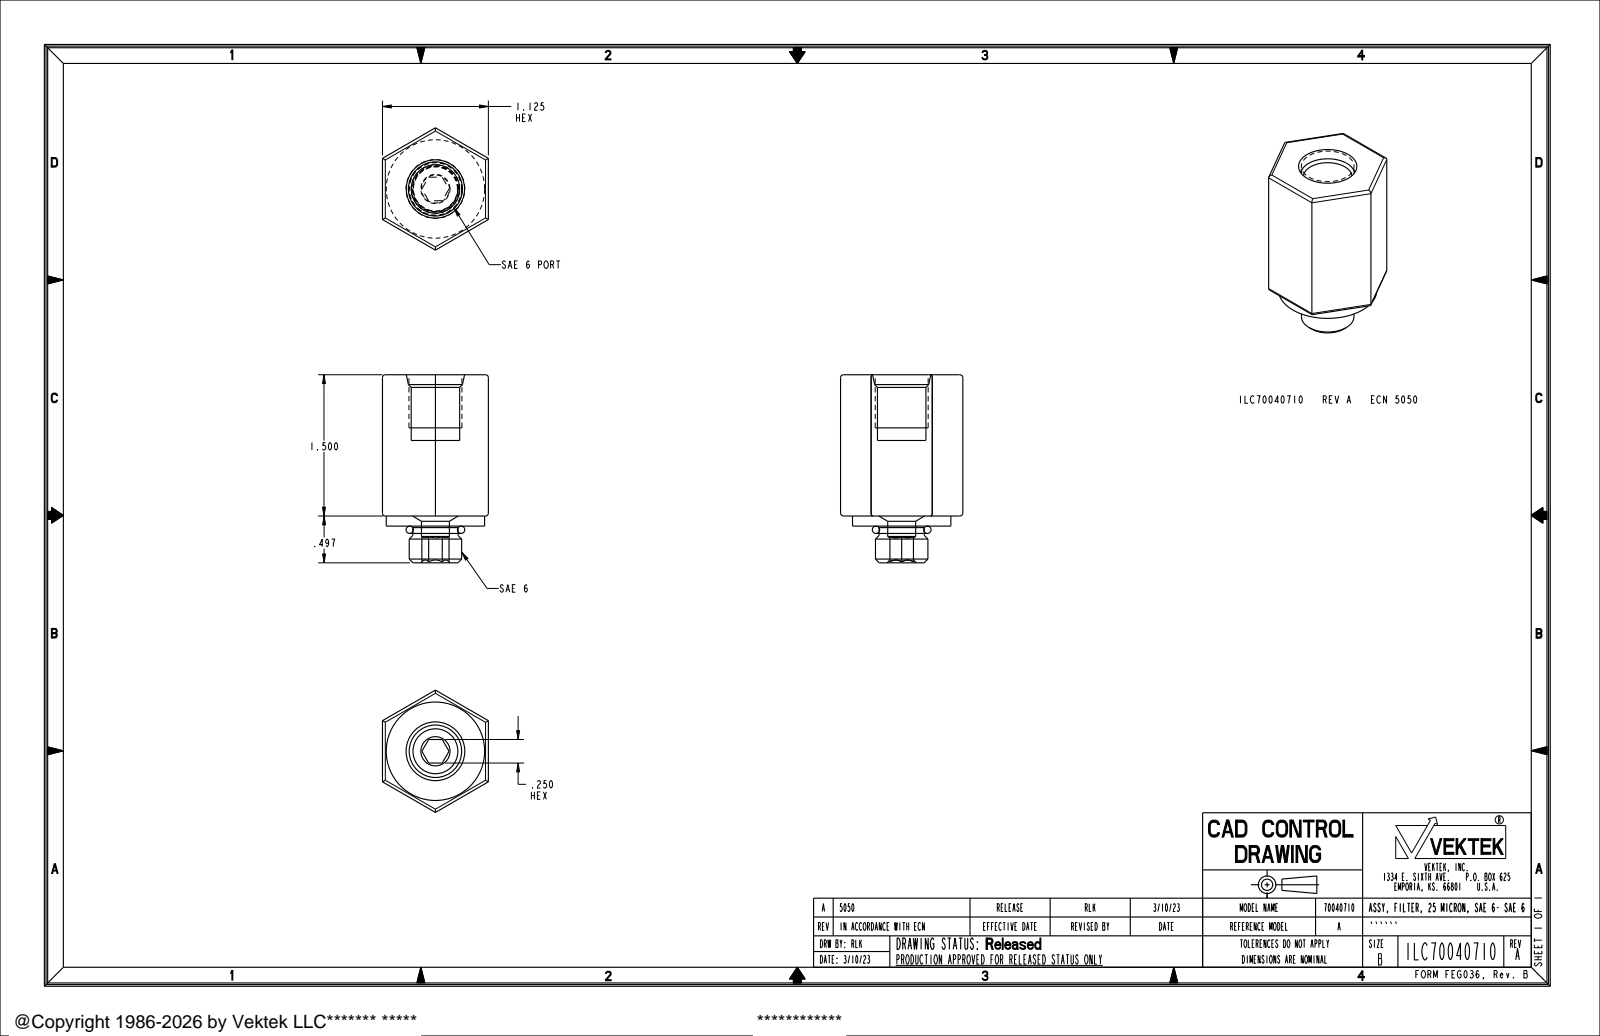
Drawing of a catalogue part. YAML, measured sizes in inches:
part_name: "ILC70040710"
step_written_by: "CREO PARAMETRIC BY PTC INC, 2021164 (AUTOMOTIVE_DESIGN)"
units: inches
bodies: {solids: 0, faces: 62, planar: 18, cylindrical: 24, other: 20}
overall_size: [1.997, 1.299, 1.125]
round_holes:
  - {diameter: 0.297, count: 1}
  - {diameter: 0.515, count: 1}
round_bosses_or_shafts:
  - {diameter: 1.045, count: 1}
  - {diameter: 0.563, count: 1}
  - {diameter: 0.557, count: 1}
  - {diameter: 0.481, count: 1}
partial_cylinders:
  - {radius: 0.03, count: 12}
face_to_face_distances: [1.125, 1.5, 0.107, 1.607, 0.909, 0.802, 0.698, 0.39, 0.497, 1.299]
